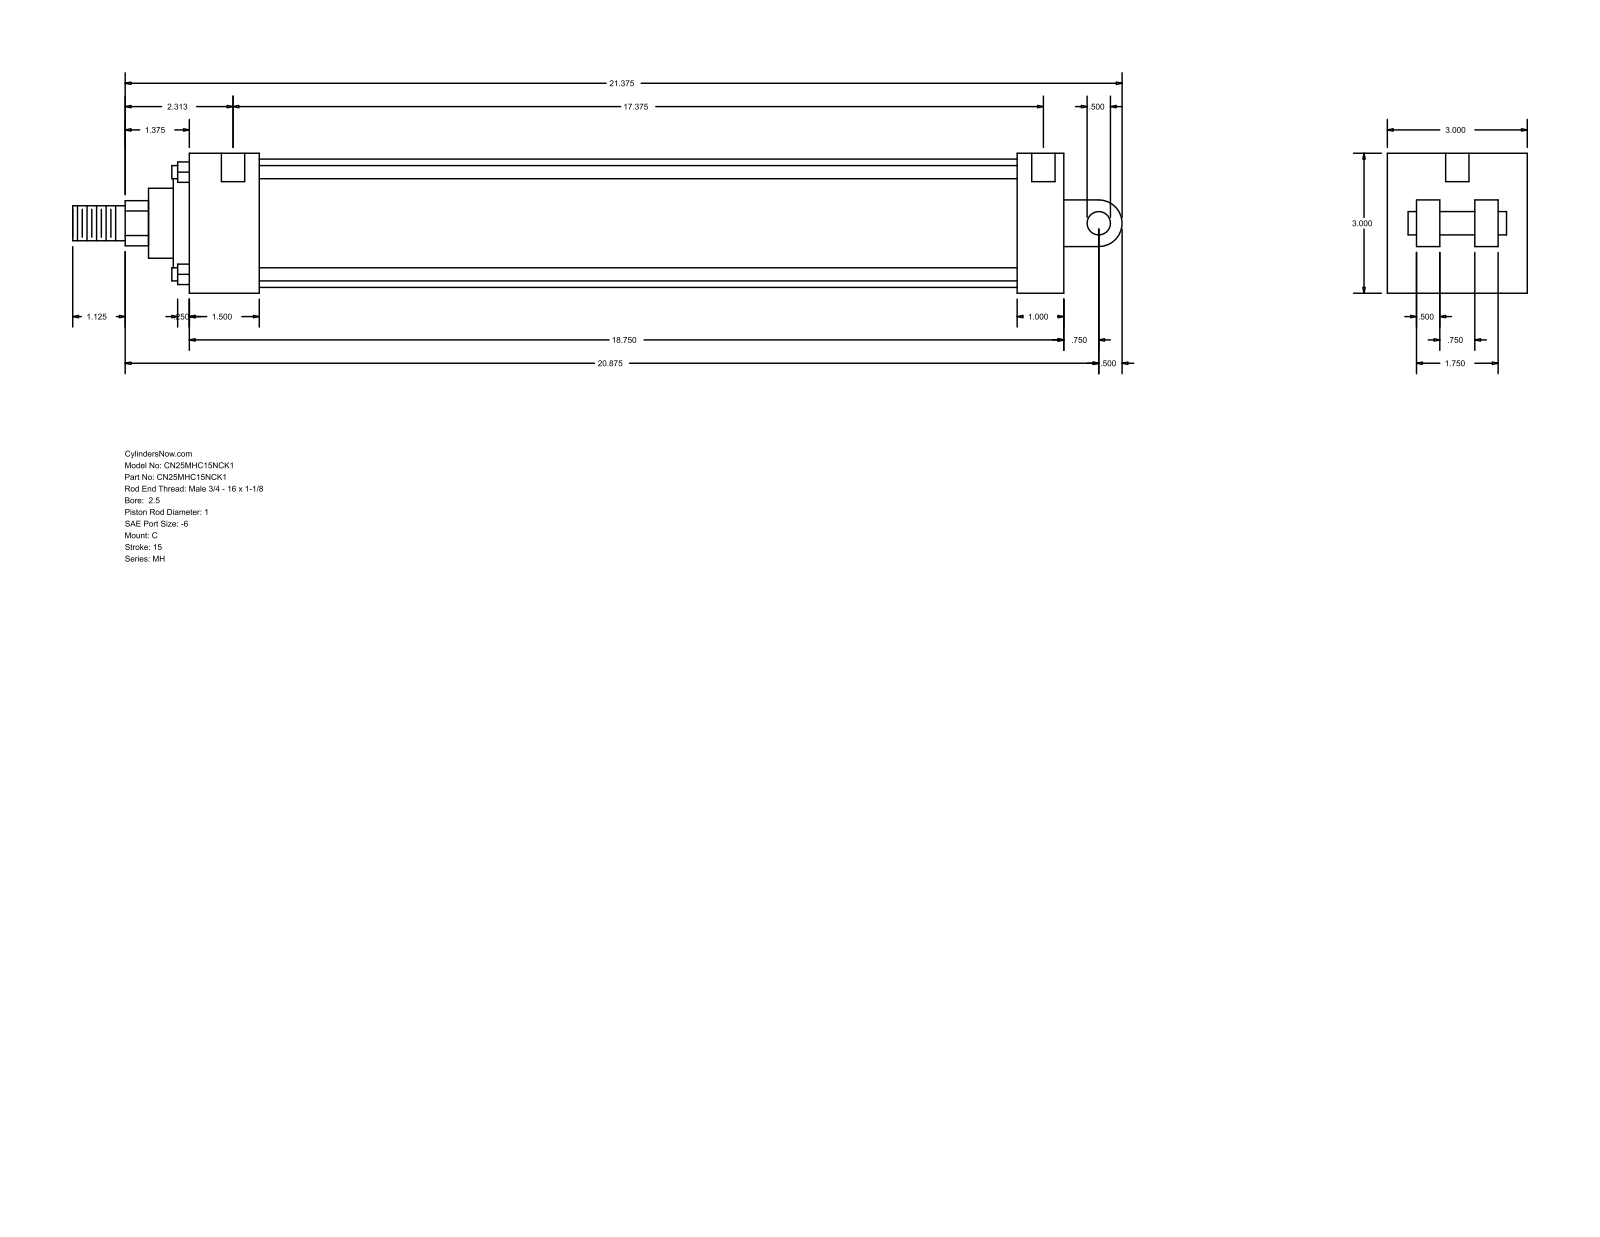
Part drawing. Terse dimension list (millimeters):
name: MH_C__0250_1
written by: GSSL Pune (CONFIG_CONTROL_DESIGN)
unit: mm
bodies: 0 solids, 101 faces (71 planar, 30 cylindrical, 0 other)
size: 571.5 × 76.2 × 76.2
holes: 4× ⌀5.56, 2× ⌀12.7
bosses: 4× ⌀7.14, 1× ⌀69.85, 1× ⌀60.33, 1× ⌀38.1, 1× ⌀25.4, 1× ⌀19.05, 1× ⌀12.7
rounds: 1× R12.29, 1× R12.7
face distances: 76.2, 476.26, 60.33, 15.87, 450.85, 25.41, 38.11, 412.74, 438.15, 12.7
hole spacings: 449.26, 3.18, 4.76, 441.32, 444.5, 446.08
